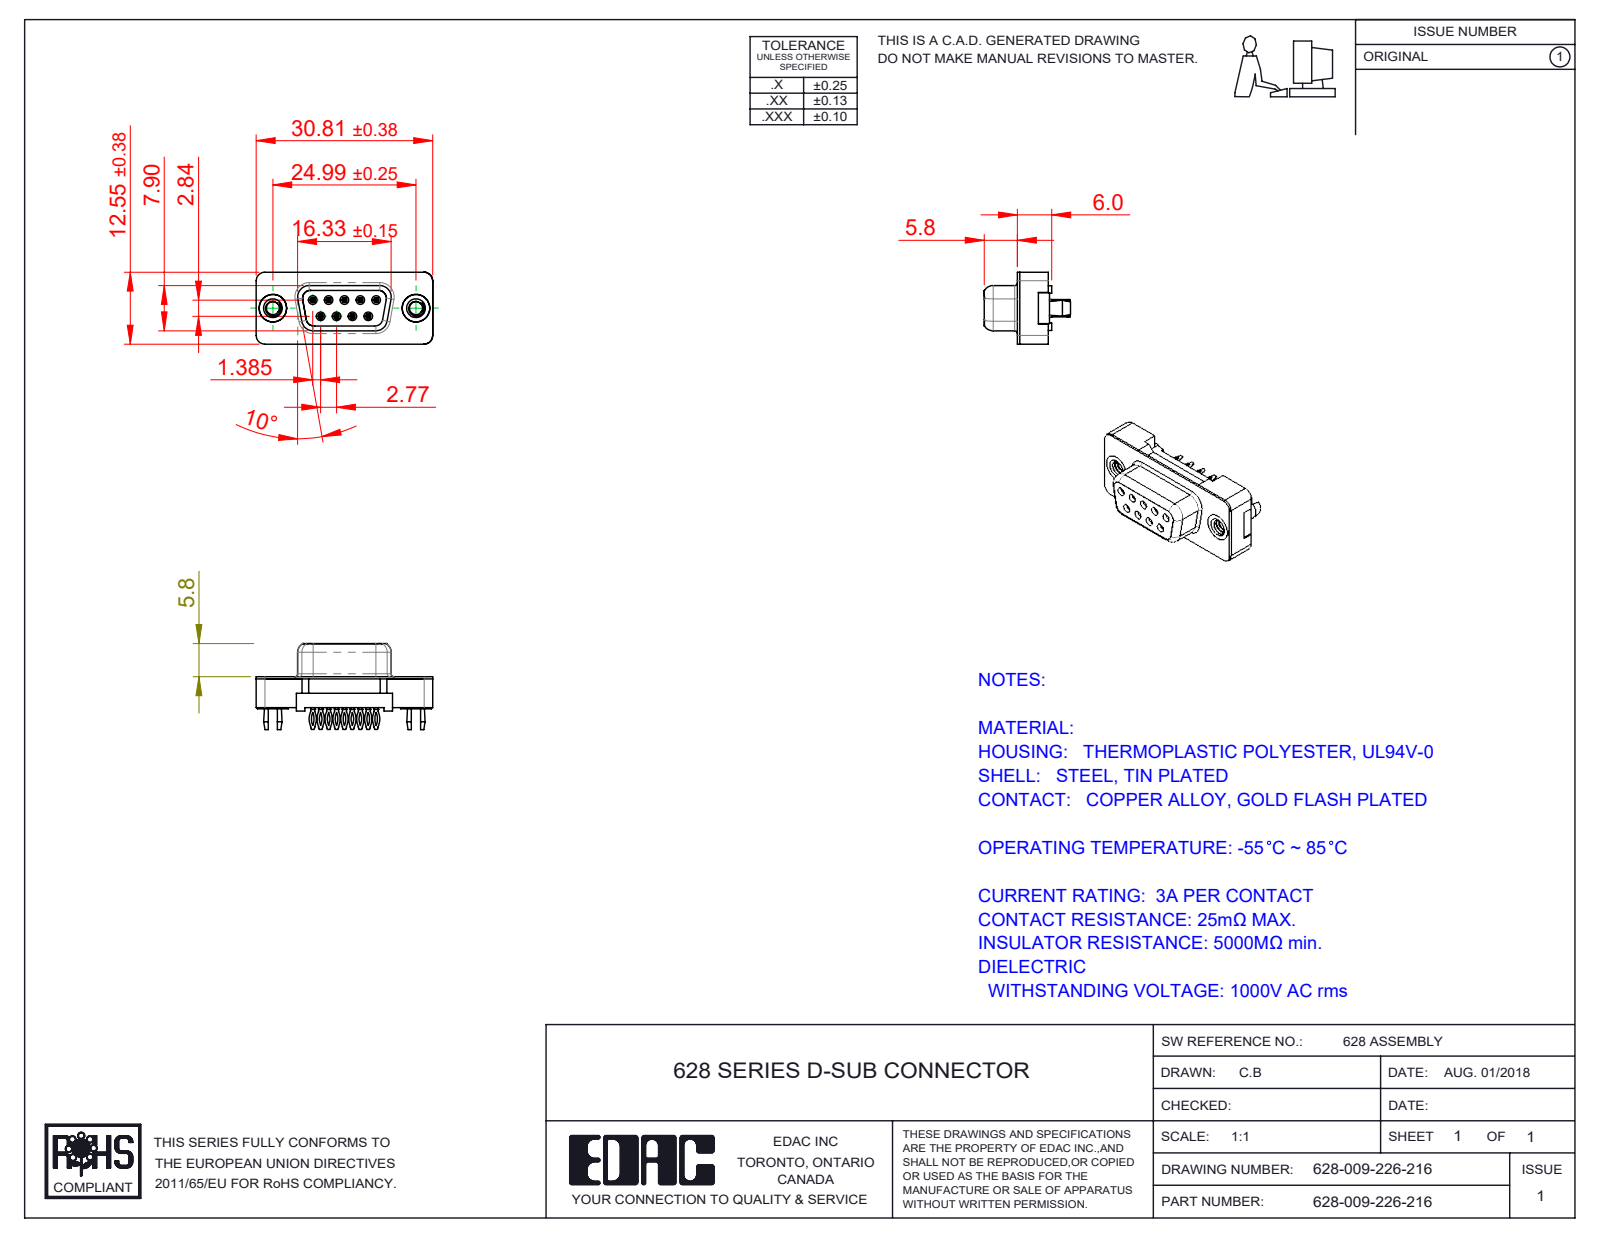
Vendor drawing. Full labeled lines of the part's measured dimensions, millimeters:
Part name (STEP PRODUCT): 628 PB 4-40 Threaded Rivet with Boardlock; 628 Plastic Body Housing_09 Contacts; 628 PB Contact Row 1_26; 628 PB Contact Row 2_26 (+2 more)
STEP written by: SolidWorks 2020 (CONFIG_CONTROL_DESIGN)
Units: millimetres
Bodies: 13 solids, 1071 faces (442 planar, 278 cylindrical, 351 other)
Overall size (bounding box): 30.82 × 15.05 × 12.55
Volume: 1 988 mm³ · Surface area: 4 430 mm²
Round holes (diameter × count): ⌀0.9 ×9, ⌀2.26 ×2, ⌀3.05 ×2, ⌀4 ×2, ⌀4.8 ×2, ⌀5 ×2
Round bosses / shafts (diameter × count): ⌀4.9 ×2
Partial cylindrical surfaces — rounded edges, fillets, slot ends (radius × count): R0.25 ×36, R2.92 ×18, R3.33 ×18, R0.5 ×13, R1.35 ×11, R0.3 ×9, R1.5 ×8, R0.9 ×4
Main face-to-face distances: 0.4, 2, 5.54, 2.77, 2.5, 5, 5.4, 6.2, 2.7, 8.7
Hole centre spacings: 3.16, 2.77, 5.54, 5.03, 5.04, 8.31, 7.1, 7.48
